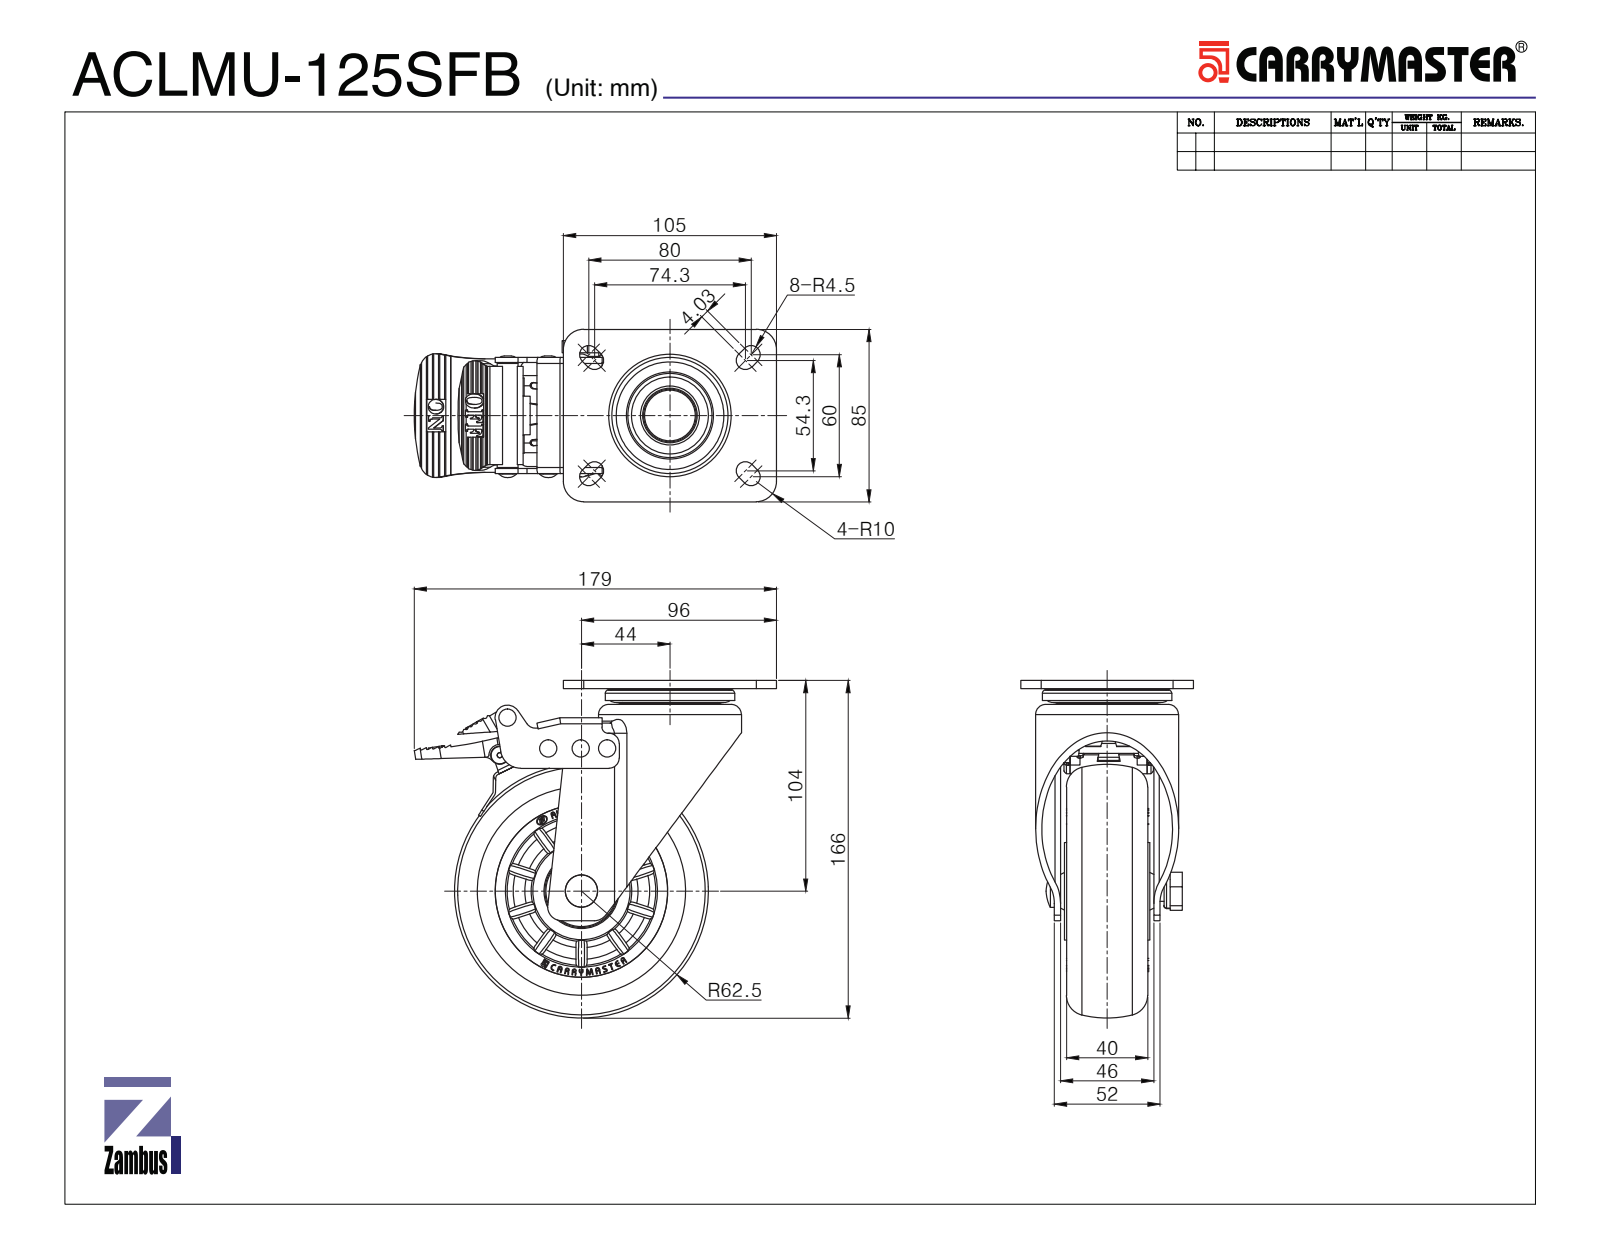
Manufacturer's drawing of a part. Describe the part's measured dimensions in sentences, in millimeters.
The part is named "ACLMU-125SFB". Its 3-D file was written by "SolidWorks 2015 (CONFIG_CONTROL_DESIGN)". It is 40 solids with 2587 faces: 1403 planar, 550 cylindrical and 634 other. Overall it measures 178.55 by 166.3 by 85 millimeters. Its volume is 591 295 cubic millimeters and its surface area 215 838 square millimeters. Round holes: 2 of diameter 1.7, 2 of diameter 3.5, 2 of diameter 4.3, 2 of diameter 5, 1 of diameter 2.5, 1 of diameter 2.6, 1 of diameter 4, 1 of diameter 5.2, 1 of diameter 5.3, 1 of diameter 8.5, 1 of diameter 10, 1 of diameter 12. Round bosses or shafts: 4 of diameter 4.9, 2 of diameter 9, 2 of diameter 6.9, 2 of diameter 0.65, 1 of diameter 105, 1 of diameter 70.42, 1 of diameter 63.7, 1 of diameter 60.5. Partial cylindrical surfaces (rounded edges, fillets, slot ends): 49 of radius 1, 24 of radius 3, 20 of radius 12, 17 of radius 1.5, 8 of radius 4.5, 7 of radius 5, 5 of radius 0.5, 5 of radius 2. The main face-to-face distances are 3, 6, 4, 46, 43, 5, 49, 40, 41, 8. The hole center spacings are 0.46, 9.31, 9.7, 12.81, 13, 16, 16.66, 18.78.
